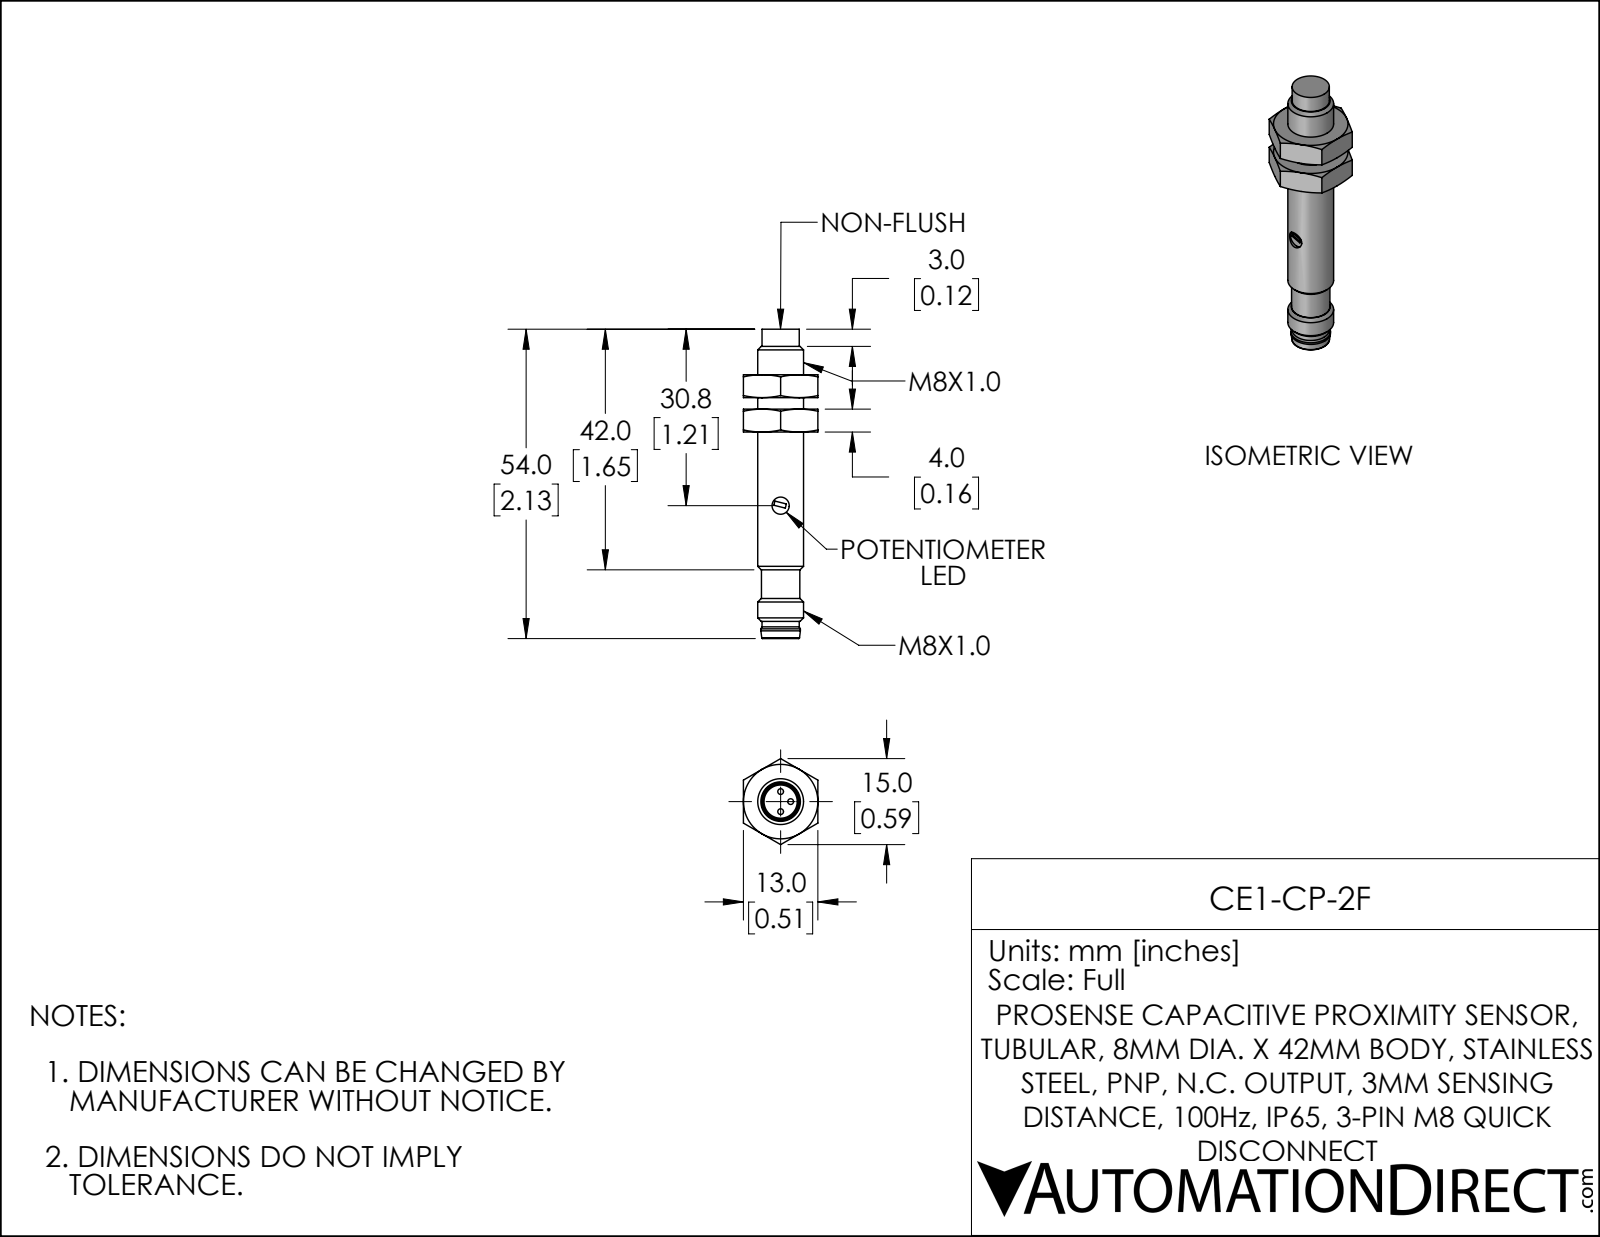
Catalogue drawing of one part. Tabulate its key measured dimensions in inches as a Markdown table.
| quantity | value |
| --- | --- |
| part name | CE1-CP-2F |
| STEP written by | SolidWorks 2019 (CONFIG_CONTROL_DESIGN) |
| units | inches |
| bodies | 3 solids, 80 faces (31 planar, 13 cylindrical, 36 other) |
| overall size | 2.126 × 0.591 × 0.512 |
| volume | 0.198 in³ |
| surface area | 3.819 in² |
| round holes (diameter × count) | 0.118 × 1, 0.228 × 1, 0.272 × 1 |
| round bosses / shafts (diameter × count) | 0.039 × 3, 0.315 × 1, 0.272 × 1, 0.264 × 1, 0.256 × 1 |
| main face-to-face distances | 0.512, 0.157, 0.236, 0.079, 0.394, 0.313, 0.47, 0.549, 0.707, 1.459 |
